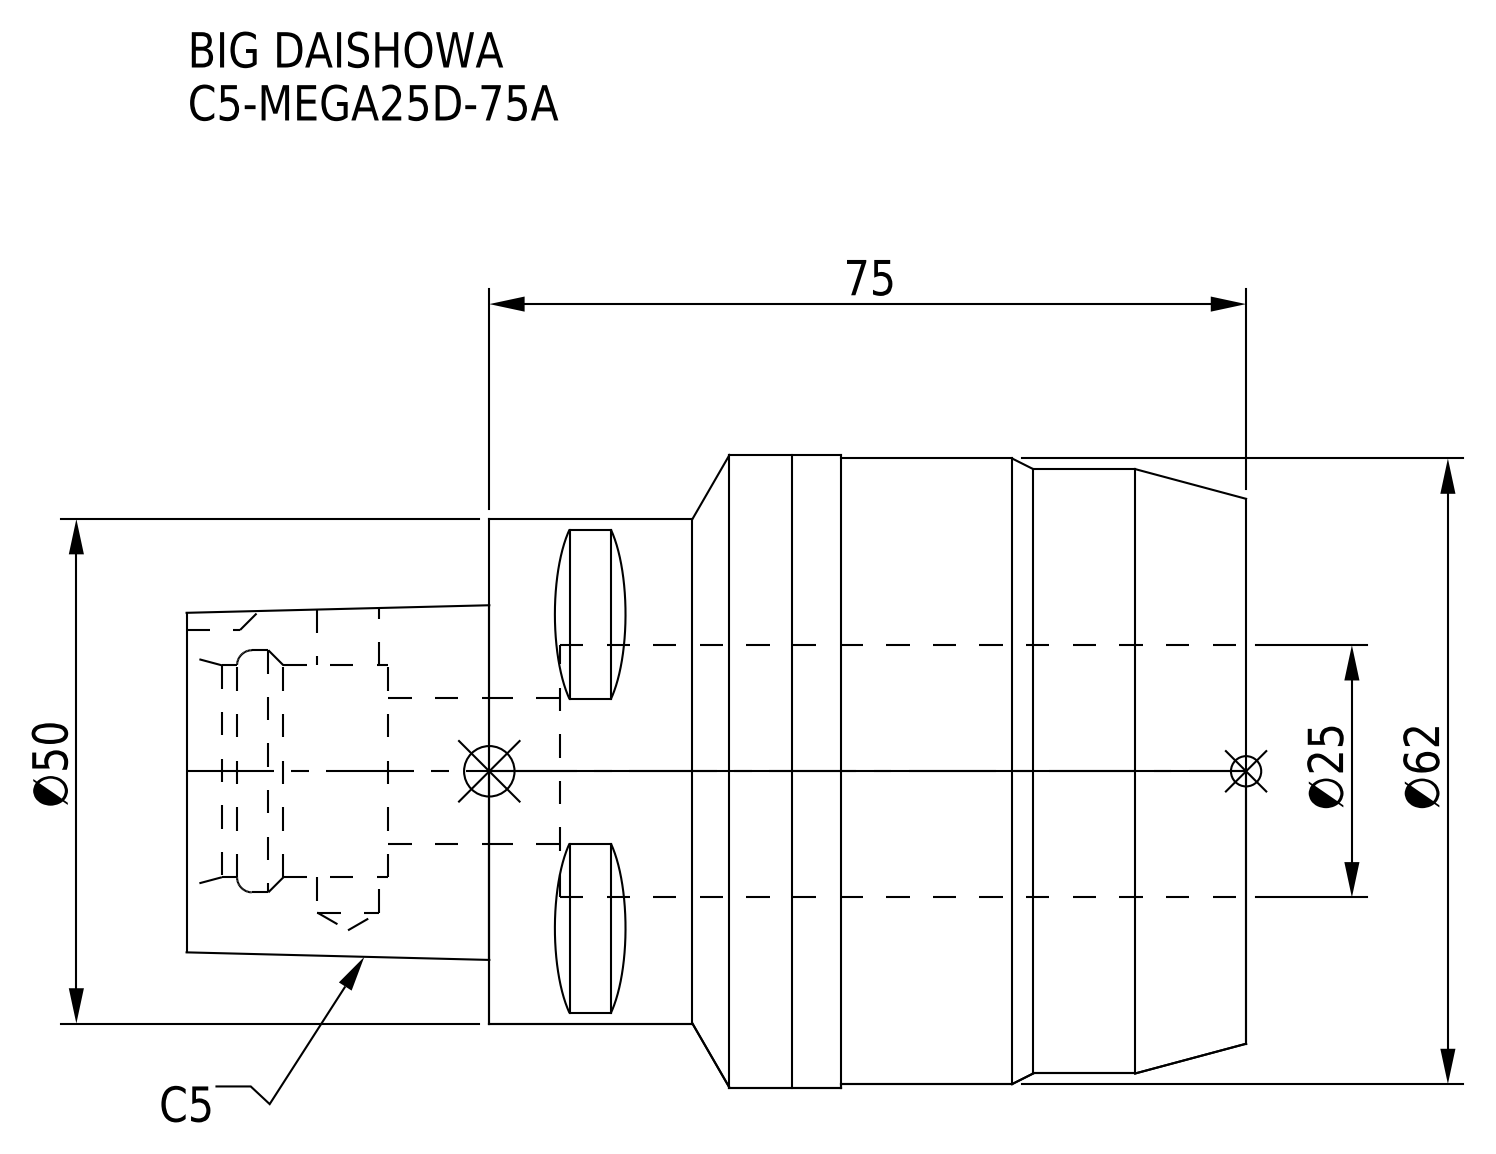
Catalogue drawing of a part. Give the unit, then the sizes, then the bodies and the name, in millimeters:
Units: millimetres
Overall size (bounding box): 105 × 62.7 × 62.7
Round holes (diameter × count): ⌀6.1 ×1, ⌀14.5 ×1, ⌀21 ×1, ⌀24 ×1, ⌀25 ×1
Round bosses / shafts (diameter × count): ⌀62.7 ×1, ⌀62 ×1, ⌀59.9 ×1, ⌀50 ×1
Partial cylindrical surfaces — rounded edges, fillets, slot ends (radius × count): R4 ×1
Main face-to-face distances: 75, 105, 30, 68, 7, 37, 44, 85, 17, 10
Volume: 179 314 mm³ · Surface area: 29 339 mm²
Bodies: 1 solid, 67 faces (28 planar, 23 cylindrical, 16 other)
Part name (STEP PRODUCT): C5-MEGA25D-75A
STEP written by: CREO PARAMETRIC BY PTC INC, 2016380 (AUTOMOTIVE_DESIGN)
